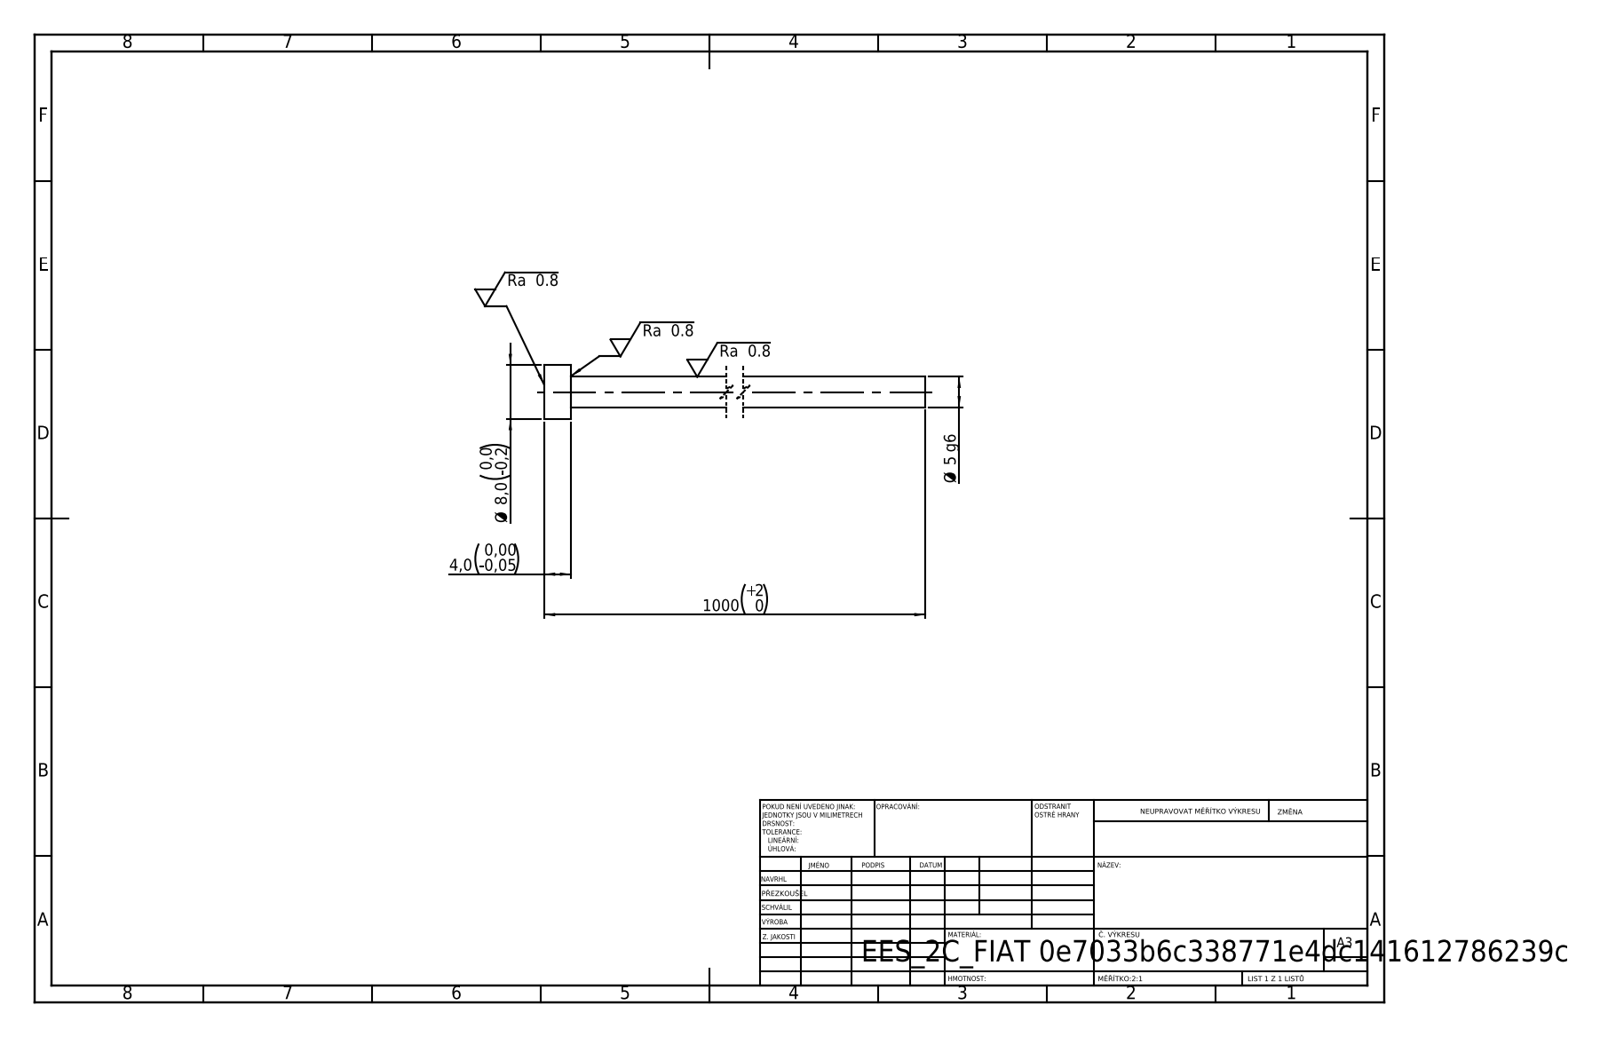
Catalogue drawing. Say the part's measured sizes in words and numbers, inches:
Its 3-D file was written by "SolidWorks 2019 (CONFIG_CONTROL_DESIGN)". It is 1 solid with 7 faces: 3 planar, 4 cylindrical and 0 other. Overall it measures 39.37 by 0.315 by 0.315 inches. Its volume is 0.979 cubic inches and its surface area 22.14 square inches. Round bosses or shafts: 1 of diameter 0.315, 1 of diameter 0.177. The main face-to-face distances are 0.157, 39.37, 39.213.
